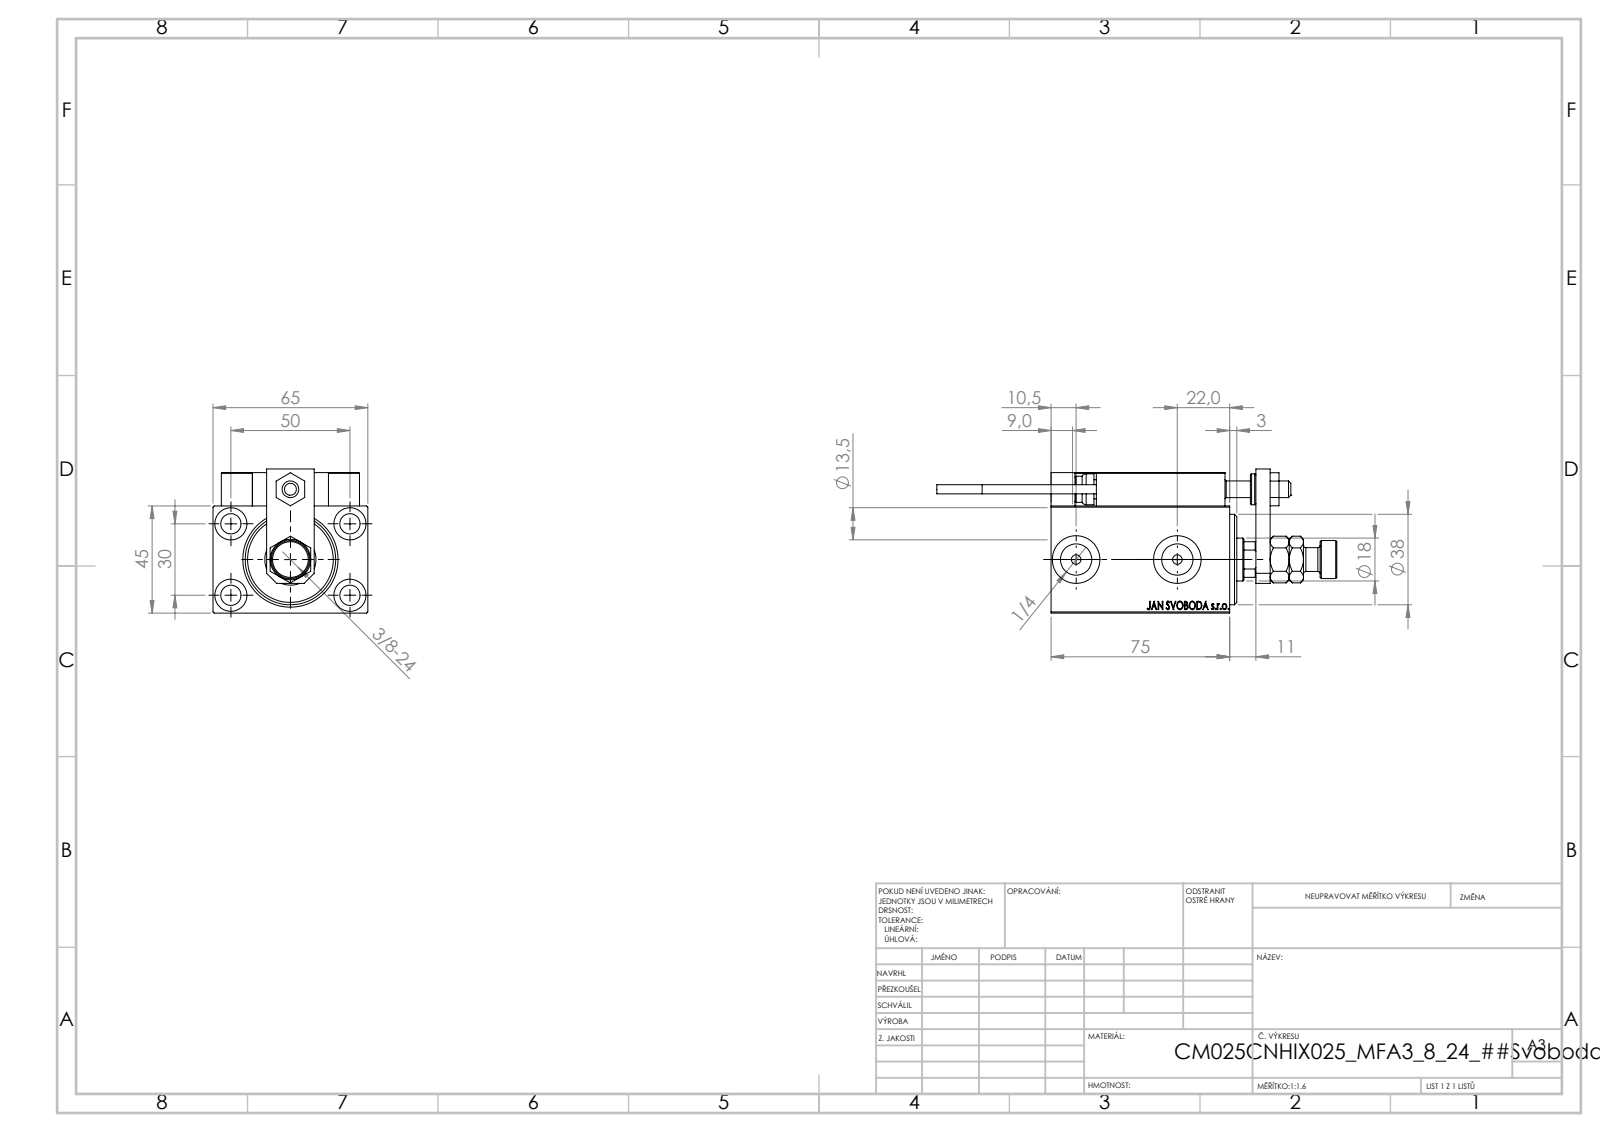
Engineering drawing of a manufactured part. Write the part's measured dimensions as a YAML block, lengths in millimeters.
part_name: "SWITCH_X_FRONT_BACK; SWITCH X; ALLEN BOLT D8; V450CM_C_Body (+7 more)"
step_written_by: "SolidWorks 2019 (CONFIG_CONTROL_DESIGN)"
units: millimeters
bodies: {solids: 24, faces: 1334, planar: 576, cylindrical: 192, other: 566}
overall_size: [168, 65, 60.5]
volume: 241093
surface_area: 73684
round_holes:
  - {diameter: 4, count: 6}
  - {diameter: 8, count: 5}
  - {diameter: 8.5, count: 5}
  - {diameter: 3.2, count: 4}
  - {diameter: 13.5, count: 4}
  - {diameter: 5, count: 2}
  - {diameter: 13.16, count: 2}
  - {diameter: 20, count: 2}
  - {diameter: 7, count: 1}
  - {diameter: 14.5, count: 1}
  - {diameter: 18, count: 1}
  - {diameter: 21.5, count: 1}
round_bosses_or_shafts:
  - {diameter: 5, count: 2}
  - {diameter: 3.8, count: 2}
  - {diameter: 16, count: 1}
  - {diameter: 13, count: 1}
  - {diameter: 11, count: 1}
  - {diameter: 10, count: 1}
partial_cylinders:
  - {radius: 0.3, count: 30}
  - {radius: 3, count: 2}
  - {radius: 8.5, count: 1}
face_to_face_distances: [45, 14, 65, 6, 59, 3, 13, 19, 86, 3.5]
hole_center_spacings: [29.15, 11.37, 20, 27.07, 28.9, 29.59, 29.69, 30]
